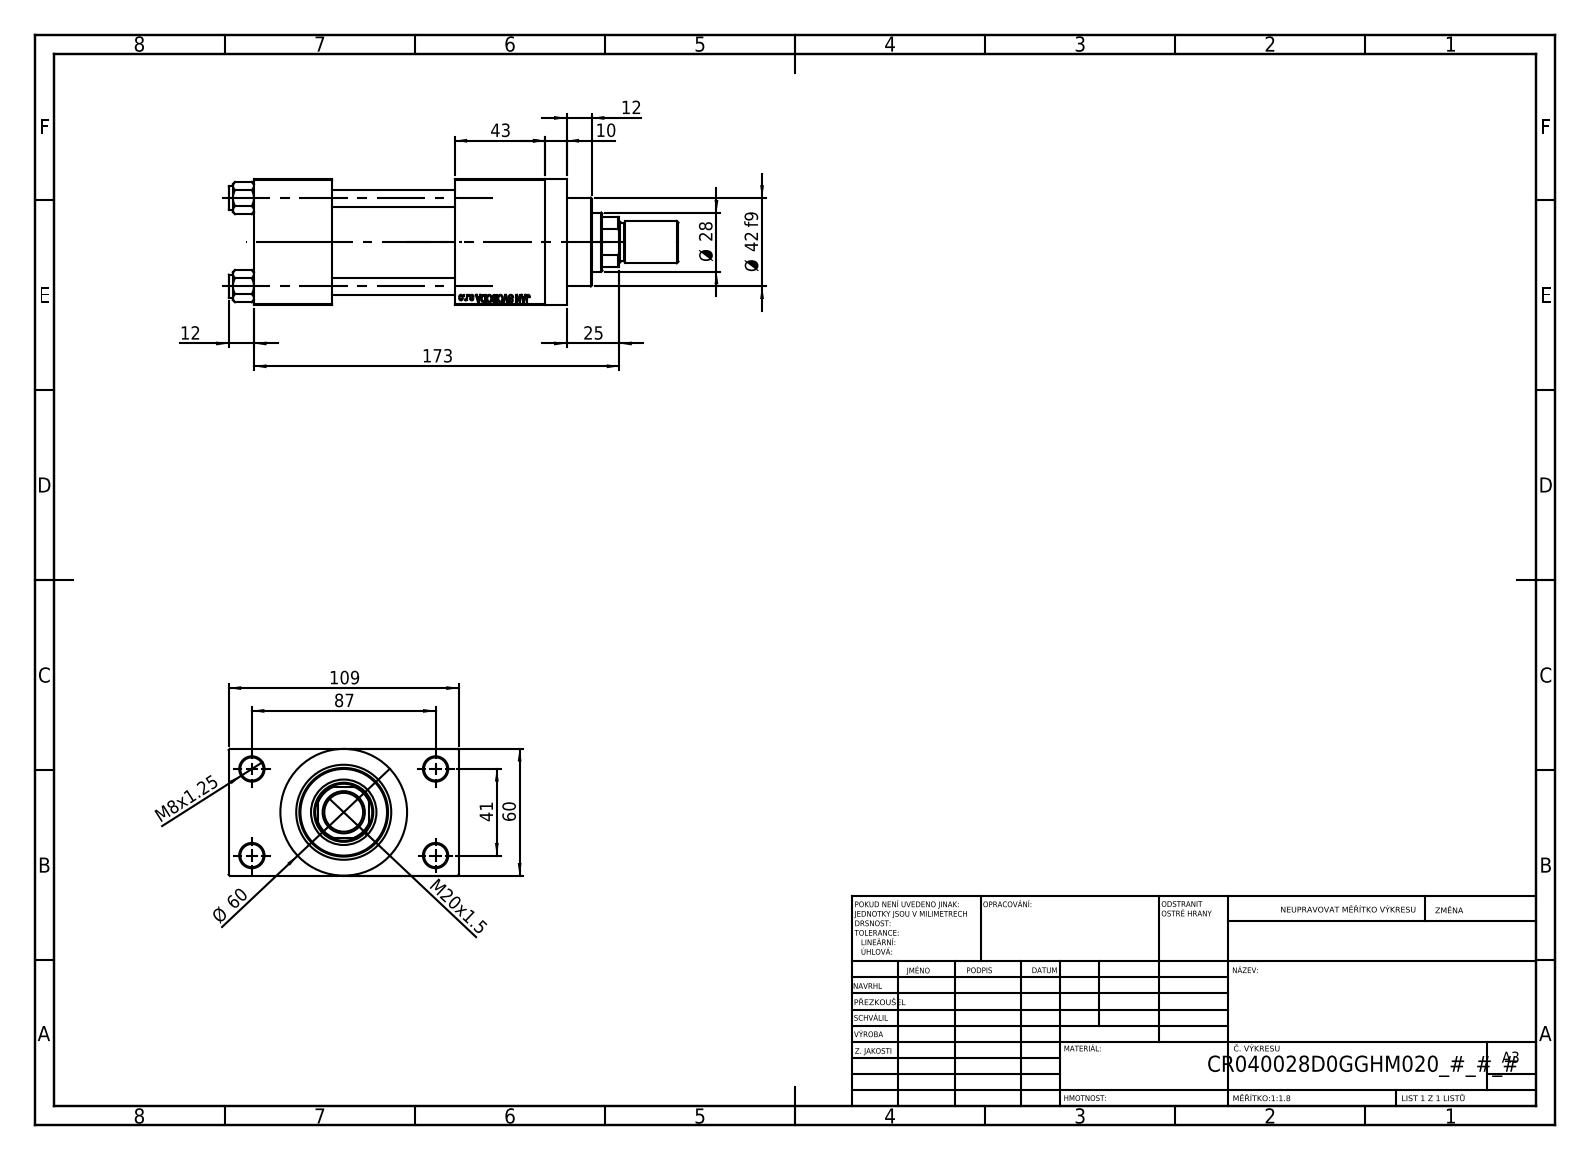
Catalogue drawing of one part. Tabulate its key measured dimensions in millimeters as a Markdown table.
| quantity | value |
| --- | --- |
| part name | V215CR_D_Body; NUT_M5_D; V215CR_D_TYCINKA; ROD_END_AH (+2 more) |
| STEP written by | SolidWorks 2019 (CONFIG_CONTROL_DESIGN) |
| units | millimeters |
| bodies | 12 solids, 1119 faces (502 planar, 93 cylindrical, 524 other) |
| overall size | 213 × 109 × 60 |
| volume | 542 773 mm³ |
| surface area | 130 260 mm² |
| round holes (diameter × count) | 8 × 4, 11 × 4, 7 × 2, 16.66 × 2, 24 × 2, 18.5 × 1, 28 × 1, 31 × 1, 40 × 1, 45 × 1 |
| round bosses / shafts (diameter × count) | 11 × 4, 60 × 1, 46 × 1, 42 × 1, 20 × 1, 18 × 1 |
| partial cylindrical surfaces (radius × count) | 13.5 × 1 |
| main face-to-face distances | 60, 84.5, 24.5, 58, 37, 95, 138, 101, 43, 109 |
| hole center spacings | 22.65, 29.49, 41.7, 47.15, 48.09, 64.35, 76.49, 41 |
